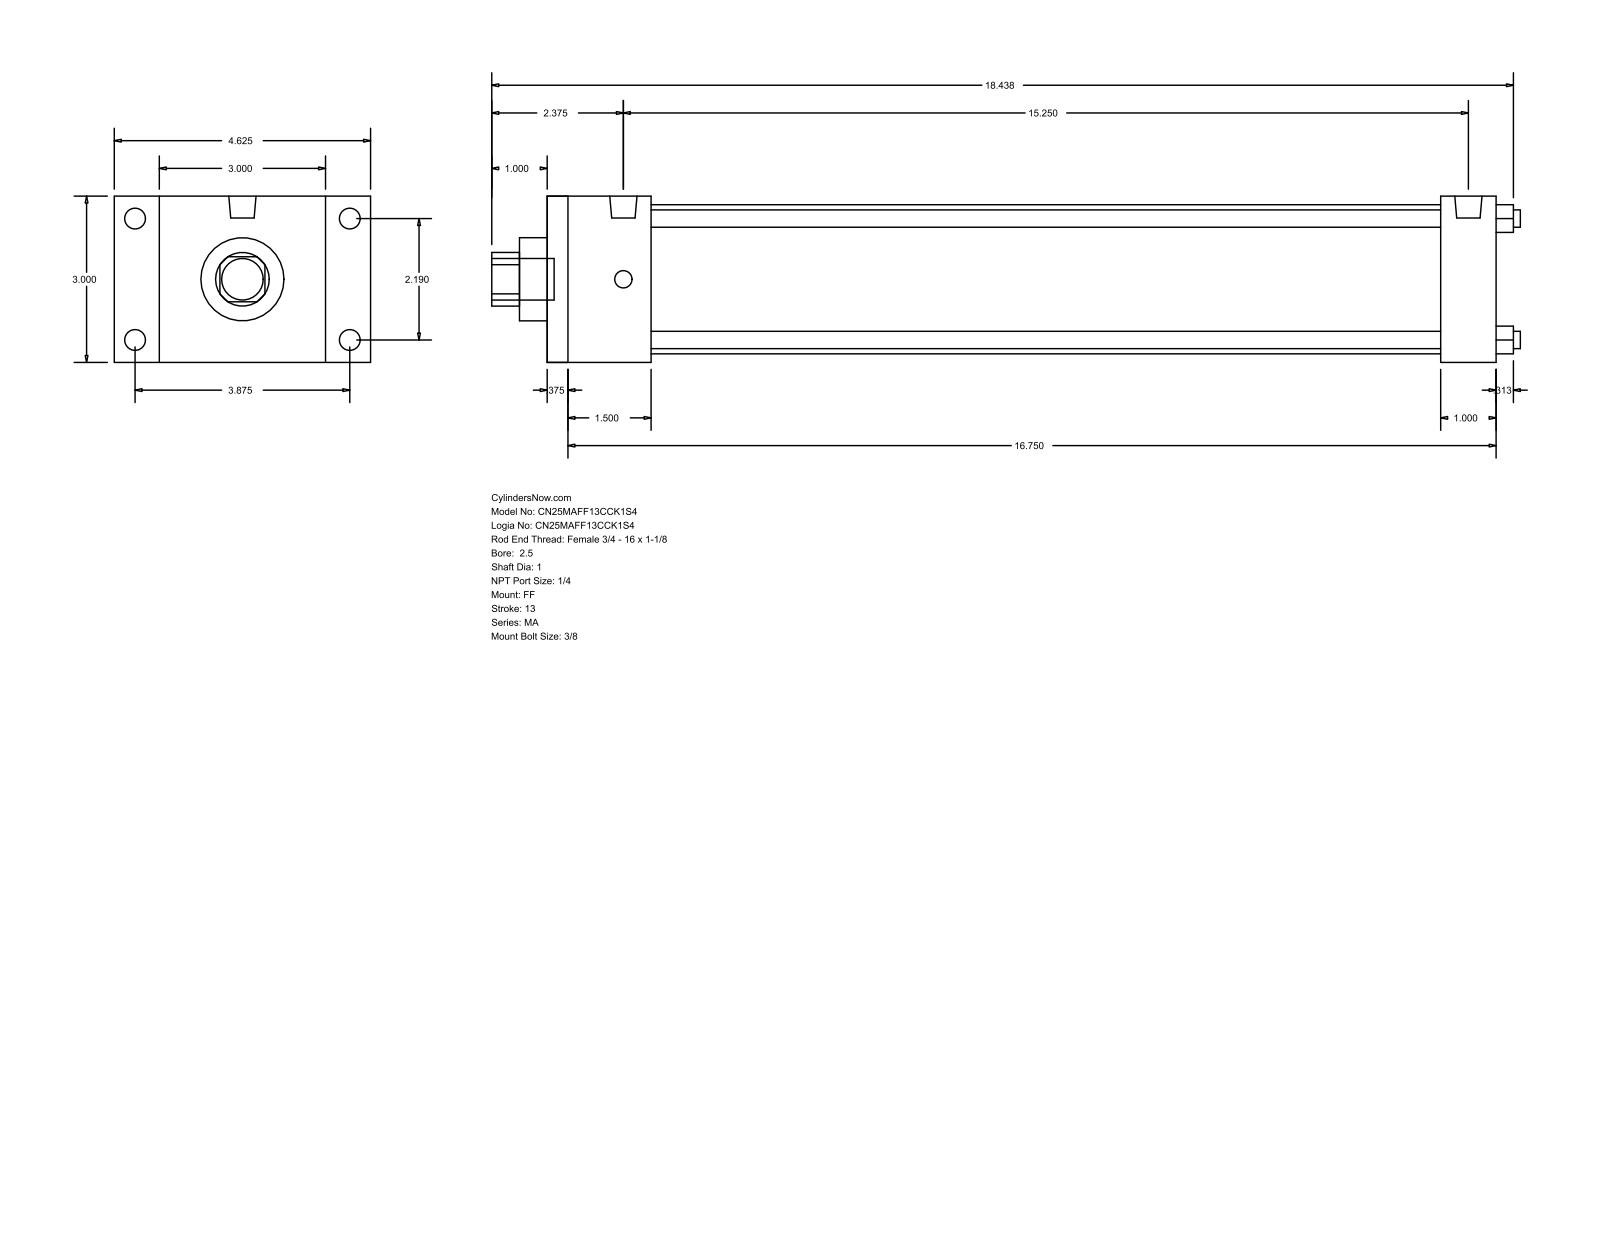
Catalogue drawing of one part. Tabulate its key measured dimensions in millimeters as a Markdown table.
| quantity | value |
| --- | --- |
| part name | MA_FF__0250_1 |
| STEP written by | GSSL Pune (CONFIG_CONTROL_DESIGN) |
| units | millimeters |
| bodies | 0 solids, 92 faces (64 planar, 28 cylindrical, 0 other) |
| overall size | 471.49 × 117.47 × 76.2 |
| round holes (diameter × count) | 7.94 × 4, 25.4 × 1, 38.1 × 1, 68.33 × 1 |
| round bosses / shafts (diameter × count) | 9.53 × 4, 7.94 × 4, 12.49 × 2, 19.05 × 1 |
| partial cylindrical surfaces (radius × count) | 12.29 × 1 |
| main face-to-face distances | 76.2, 434.98, 9.52, 425.46, 25.4, 47.63, 409.58, 38.11, 400.06, 361.95 |
| hole center spacings | 39.33, 55.62, 78.66 |
